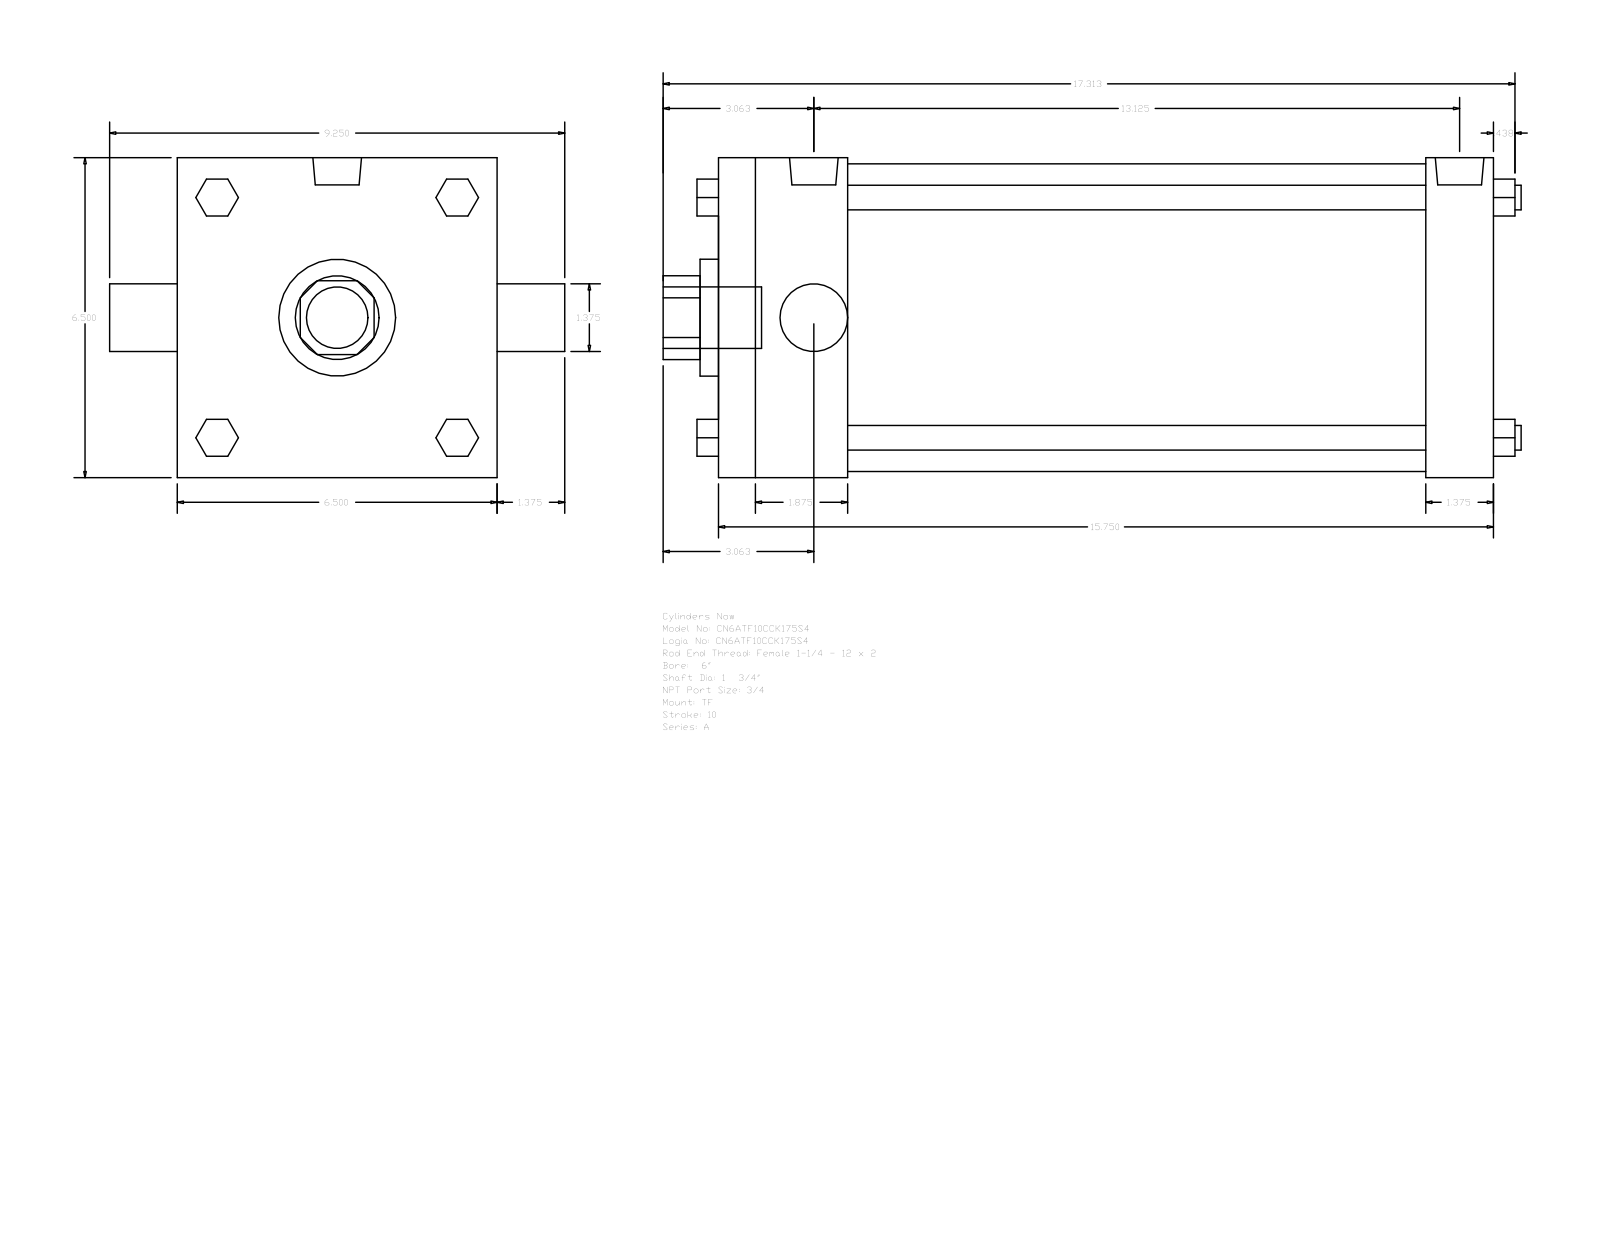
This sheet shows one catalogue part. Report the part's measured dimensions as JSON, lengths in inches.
{"part_name": "A_TF__0600_1.75", "step_written_by": "GSSL Pune (CONFIG_CONTROL_DESIGN)", "units": "inches", "bodies": {"solids": 0, "faces": 120, "planar": 92, "cylindrical": 28, "other": 0}, "overall_size": [17.437, 9.25, 6.5], "round_holes": [[1.375, 1], [1.75, 1], [2.375, 1], [6.25, 1]], "round_bosses_or_shafts": [[0.5, 4], [0.594, 3], [0.989, 2], [1.25, 1]], "partial_cylinders_radius": [[0.852, 1]], "face_to_face_distances": [6.5, 15.75, 1.375, 2.625, 13.125, 14.375, 11.75, 0.75, 2.44, 4.226]}
